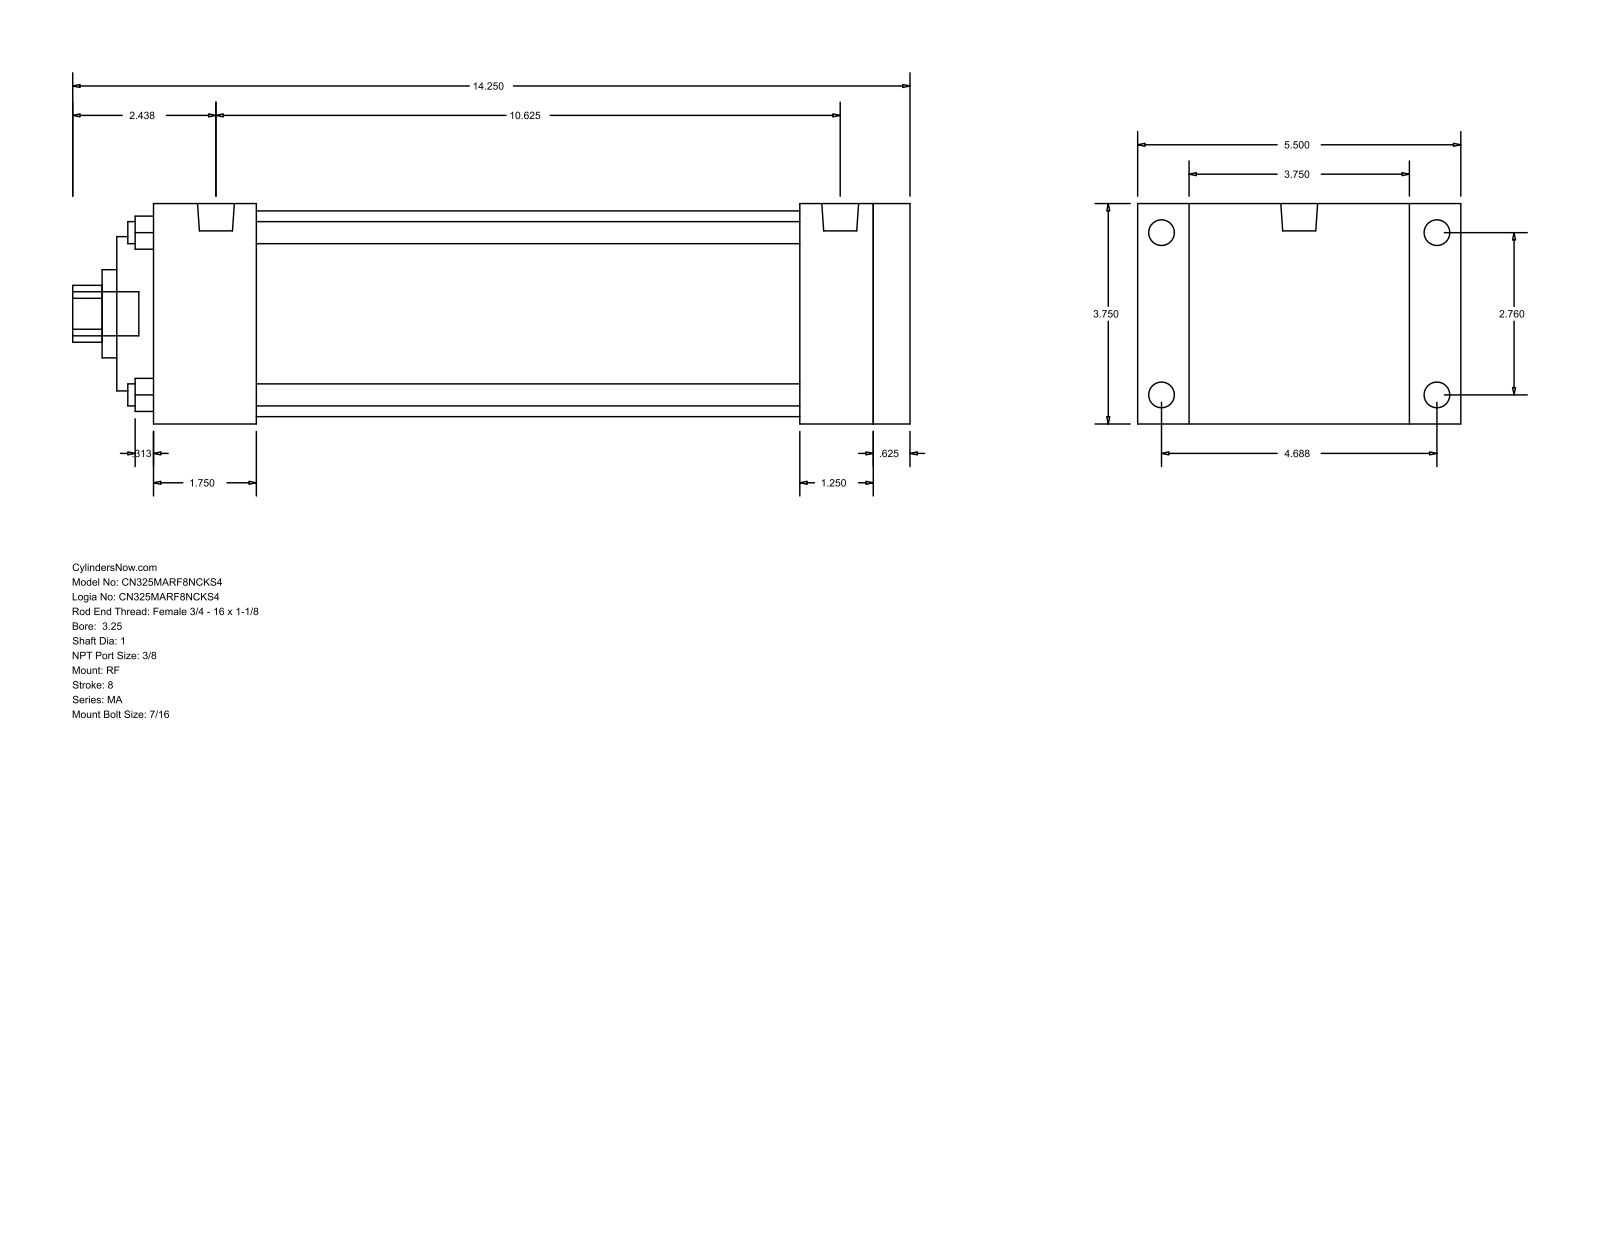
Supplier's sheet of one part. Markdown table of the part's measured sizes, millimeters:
| quantity | value |
| --- | --- |
| part name | MA_RF__0325_1 |
| STEP written by | GSSL Pune (CONFIG_CONTROL_DESIGN) |
| units | millimeters |
| bodies | 0 solids, 94 faces (65 planar, 29 cylindrical, 0 other) |
| overall size | 361.95 × 139.7 × 95.25 |
| round holes (diameter × count) | 9.53 × 4, 25.4 × 1, 38.1 × 1, 66.67 × 1, 88.9 × 1 |
| round bosses / shafts (diameter × count) | 11.11 × 8, 15.93 × 2, 19.05 × 1 |
| partial cylindrical surfaces (radius × count) | 12.29 × 1 |
| main face-to-face distances | 95.24, 327.03, 311.15, 15.88, 22.23, 117.47, 15.87, 279.4, 31.75, 47.63 |
| hole center spacings | 49.57, 70.1, 99.14 |
